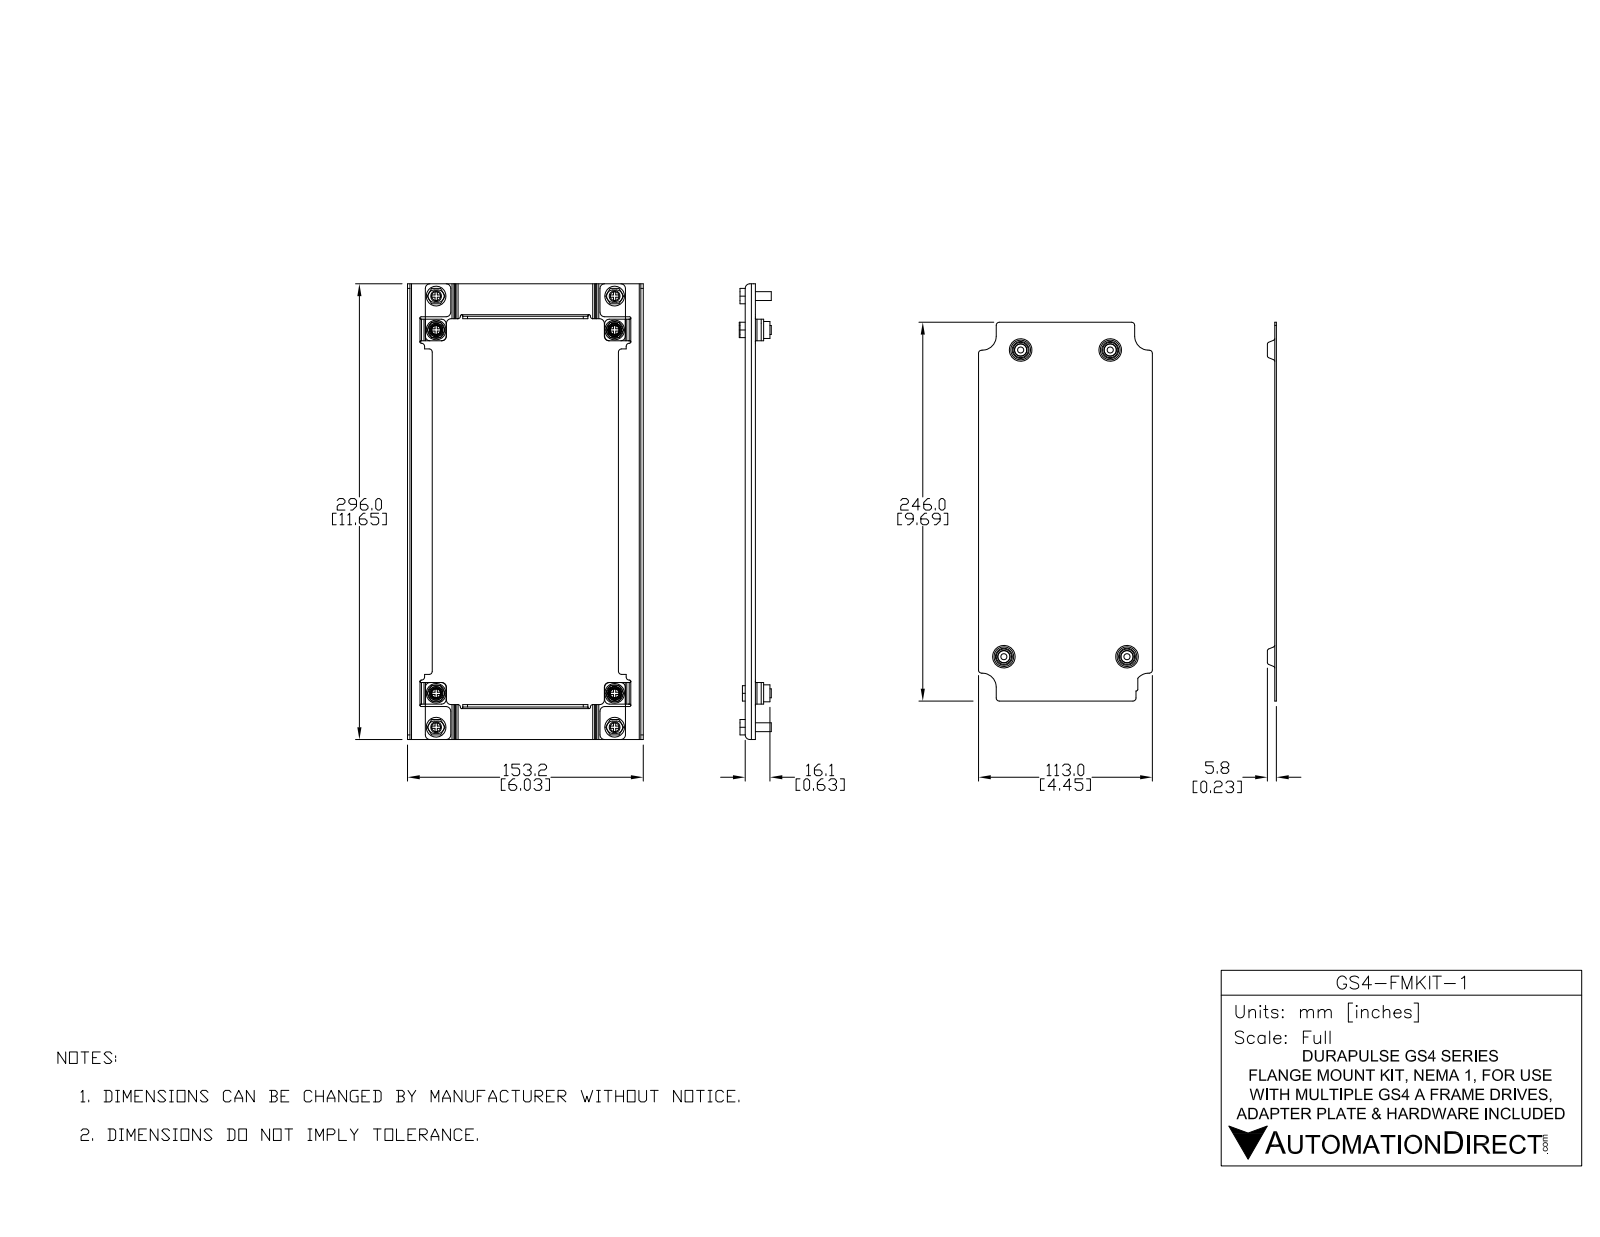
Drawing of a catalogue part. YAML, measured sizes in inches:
part_name: "GS4-FMKIT-1"
step_written_by: "SolidWorks 2015 (AUTOMOTIVE_DESIGN)"
units: inches
bodies: {solids: 0, faces: 439, planar: 209, cylindrical: 162, other: 68}
overall_size: [11.654, 6.031, 2.224]
round_holes:
  - {diameter: 0.157, count: 4}
  - {diameter: 0.504, count: 2}
round_bosses_or_shafts:
  - {diameter: 0.228, count: 8}
  - {diameter: 0.504, count: 6}
  - {diameter: 0.435, count: 4}
partial_cylinders:
  - {radius: 0.118, count: 36}
  - {radius: 0.079, count: 20}
  - {radius: 0.039, count: 9}
  - {radius: 0.102, count: 8}
  - {radius: 0.157, count: 8}
  - {radius: 0.063, count: 4}
  - {radius: 0.142, count: 4}
  - {radius: 0.354, count: 4}
face_to_face_distances: [0.039, 0.063, 1.874, 1.835, 1.811, 1.772, 5.969, 1.937, 1.898, 0.126]
hole_center_spacings: [1.175, 3.97, 7.854, 8.301, 8.853, 9.426, 2.291, 3.15]
